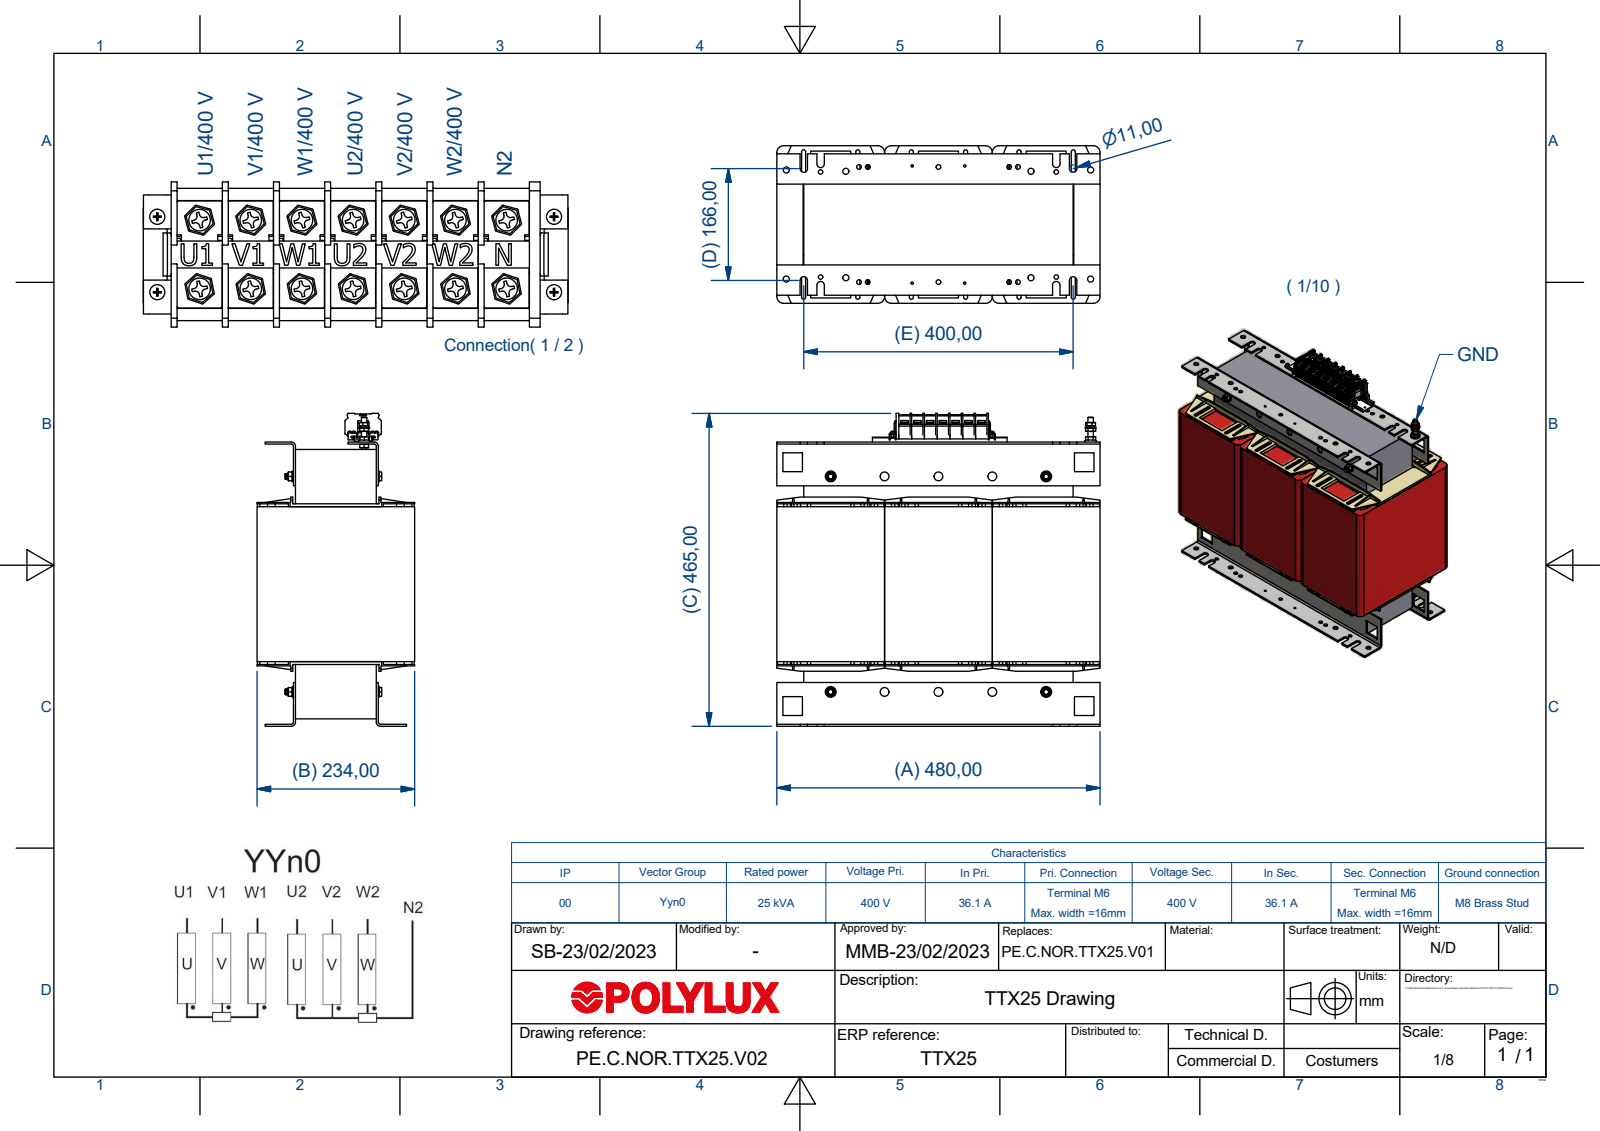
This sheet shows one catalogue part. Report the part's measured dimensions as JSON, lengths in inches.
{"part_name": "TTX25", "step_written_by": "Autodesk Inventor 2018 (AUTOMOTIVE_DESIGN)", "units": "inches", "bodies": {"solids": 106, "faces": 7971, "planar": 2923, "cylindrical": 2991, "other": 2057}, "overall_size": [18.898, 18.233, 9.213], "volume_in3": 2108, "surface_area_in2": 4791, "round_holes": [[0.354, 16], [0.276, 15], [0.197, 14], [0.209, 14], [0.213, 14], [0.315, 14], [0.262, 11], [0.512, 10], [0.138, 6], [0.165, 2], [0.175, 2], [0.167, 1]], "round_bosses_or_shafts": [[0.394, 14], [0.362, 14], [0.303, 14], [0.23, 14], [0.63, 5], [0.315, 5], [0.154, 4], [0.118, 4]], "partial_cylinders_radius": [[0.006, 1208], [0.02, 132], [0.004, 80], [0.059, 56], [0.118, 28], [0.039, 20], [0.022, 14], [0.217, 12]], "face_to_face_distances": [6.299, 12.598, 1.358, 4.941, 4.724, 4.961, 0.118, 0.039, 0.236, 11.24], "hole_center_spacings": [3.15, 12.986, 12.598, 4.134, 6.299, 14.085, 0.512, 4.646]}
